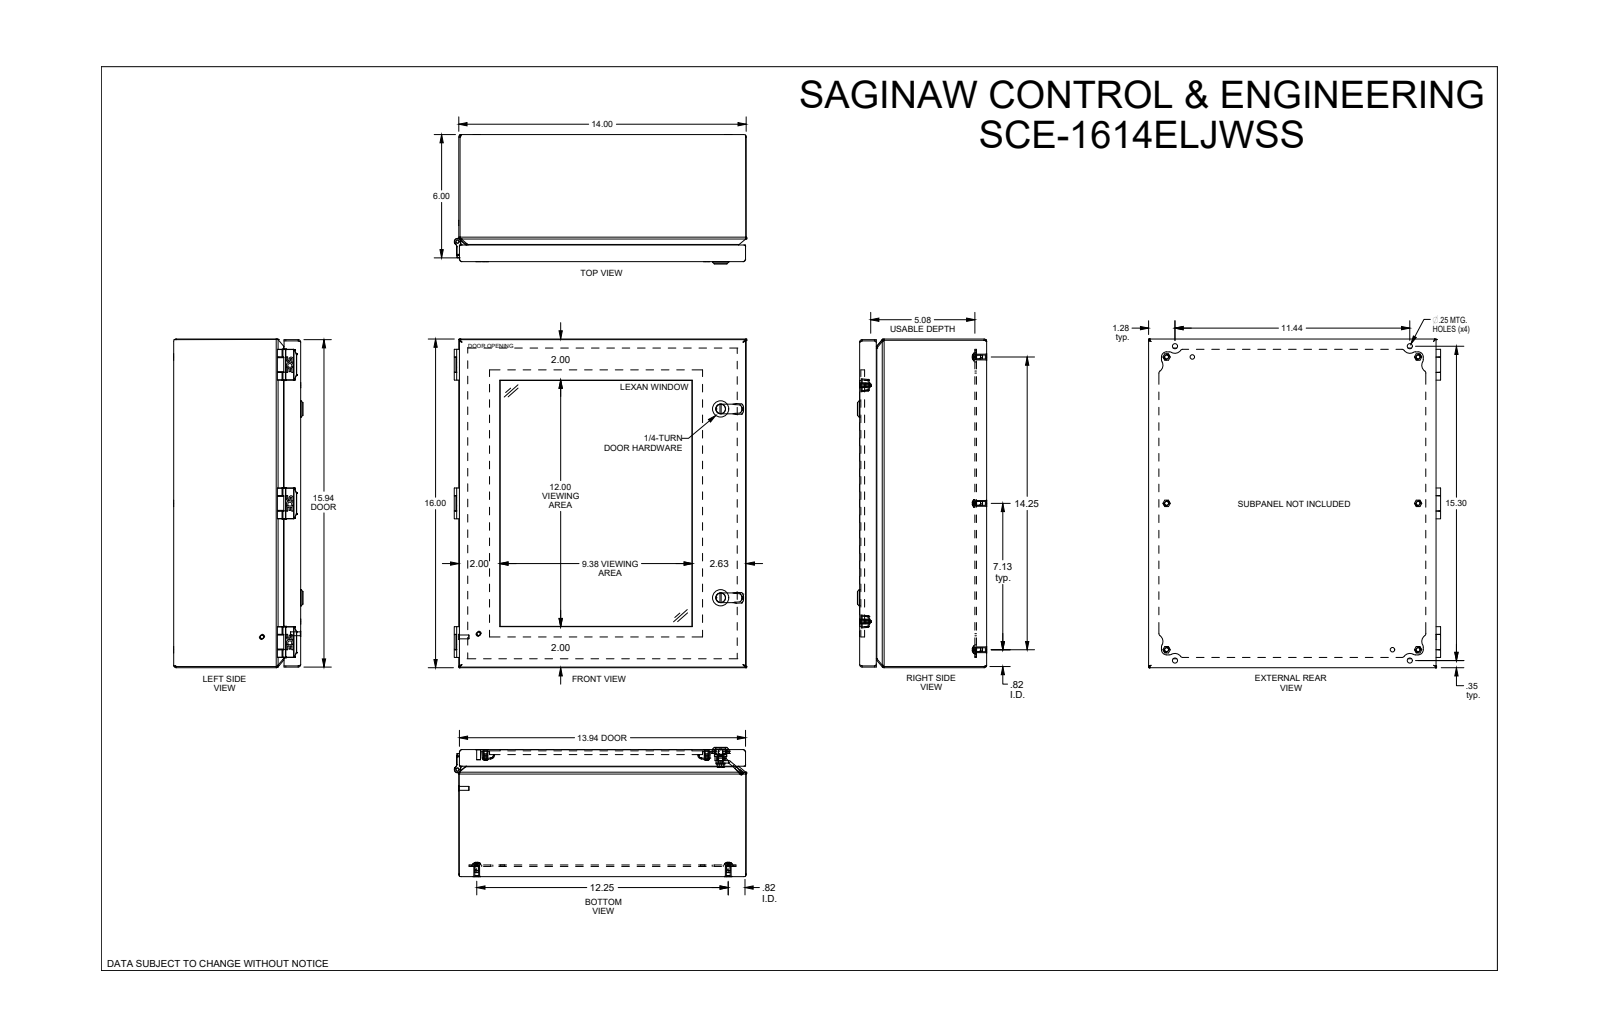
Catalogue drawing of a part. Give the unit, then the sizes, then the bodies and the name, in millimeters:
Units: millimetres
Overall size (bounding box): 407.9 × 361.2 × 159.9
Round holes (diameter × count): ⌀4.3 ×6, ⌀4.8 ×6, ⌀6.4 ×6, ⌀7.2 ×4, ⌀6.8 ×3, ⌀5.1 ×2, ⌀5.5 ×2, ⌀6.1 ×2, ⌀6.5 ×2, ⌀6.8 ×2, ⌀7.2 ×2, ⌀8.3 ×2
Round bosses / shafts (diameter × count): ⌀4.8 ×8, ⌀12.2 ×6, ⌀9.5 ×6, ⌀7.1 ×6, ⌀20 ×2, ⌀13.9 ×2, ⌀11.7 ×2, ⌀10.9 ×2
Partial cylindrical surfaces — rounded edges, fillets, slot ends (radius × count): R2.7 ×198, R0.1 ×114, R0.6 ×36, R0.8 ×16, R1.3 ×16, R0.3 ×14, R6.4 ×13, R1.5 ×12
Main face-to-face distances: 1.5, 14.5, 13, 12.6, 11.1, 1.9, 355.6, 1.5, 406.4, 151
Hole centre spacings: 171.5, 181, 359.9, 311.2, 342.9, 363.5, 1.5, 31.8
Volume: 1 537 000 mm³ · Surface area: 1 455 000 mm²
Bodies: 42 solids, 2599 faces (728 planar, 682 cylindrical, 1189 other)
Part name (STEP PRODUCT): SCE-1614ELJW
STEP written by: SolidWorks 2019 (AUTOMOTIVE_DESIGN)
